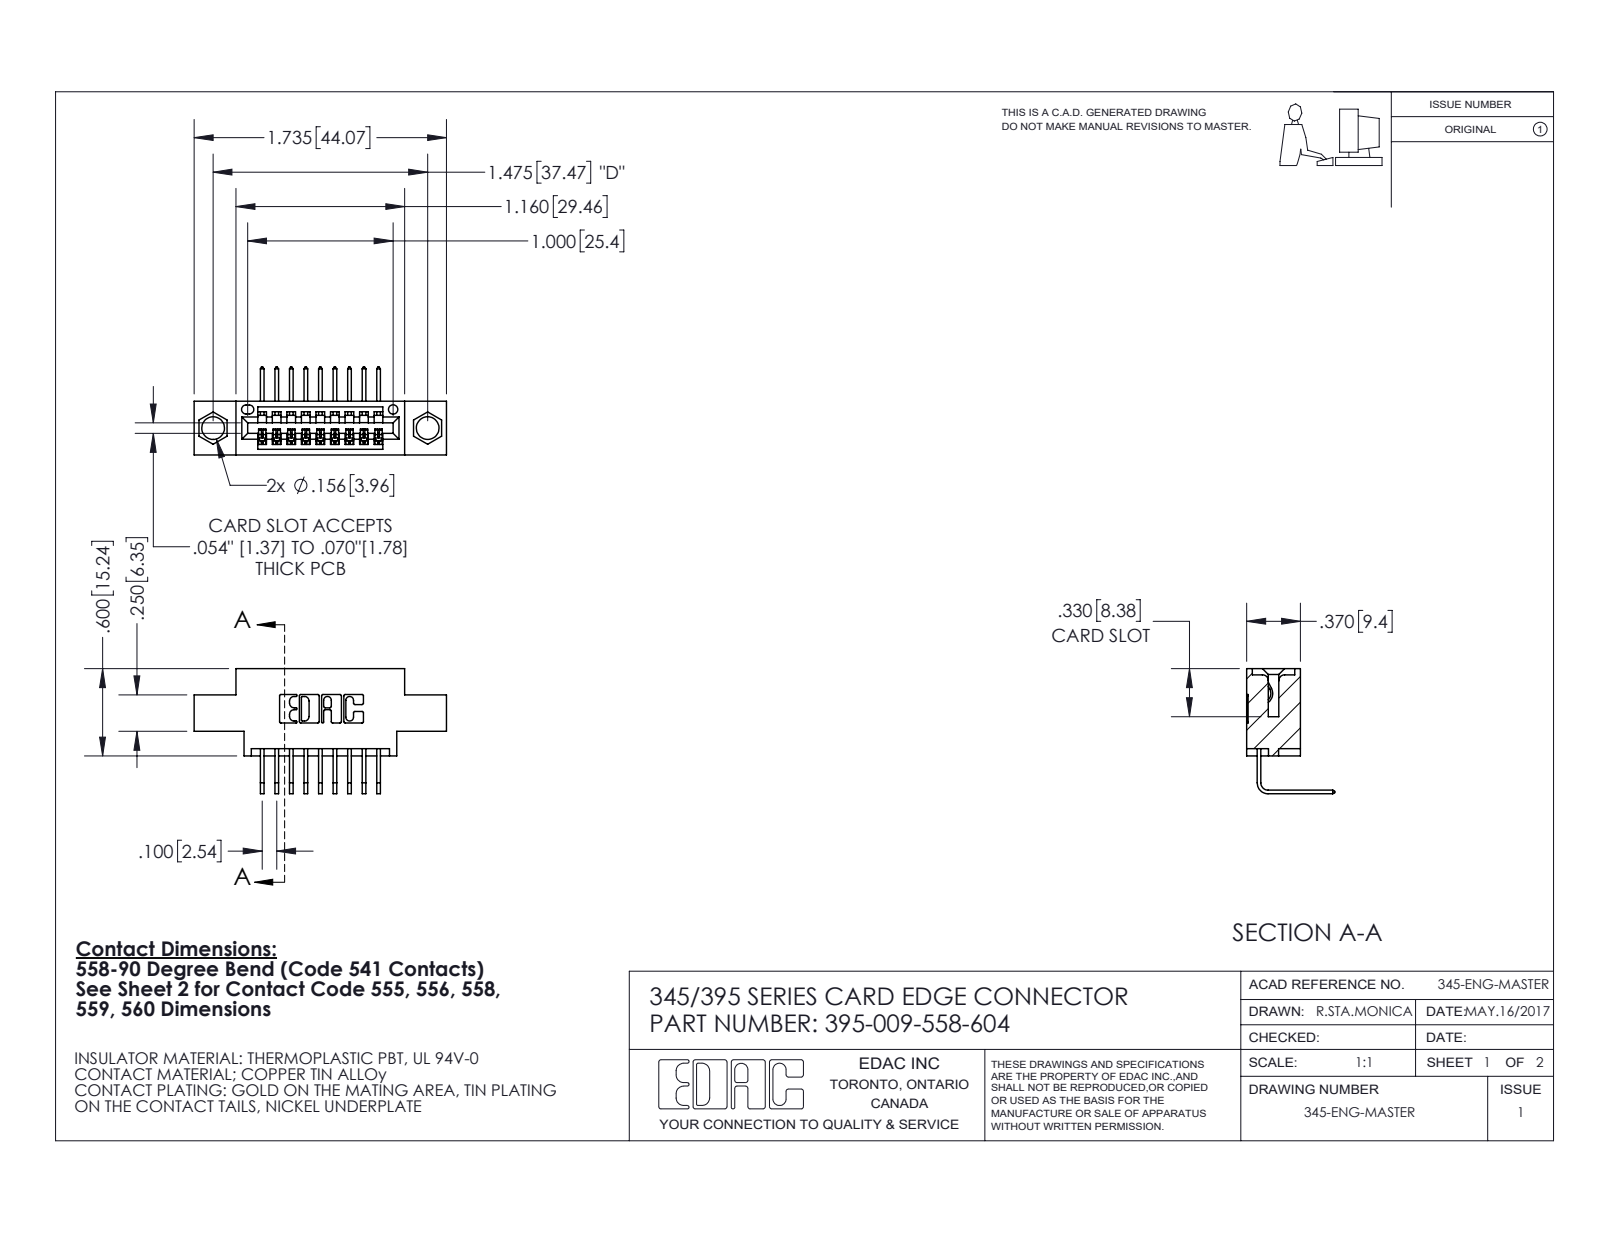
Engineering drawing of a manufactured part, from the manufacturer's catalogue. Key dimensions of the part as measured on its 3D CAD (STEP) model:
Part name (STEP PRODUCT): 345-292-001_558 Tail - 2; 345 Part_0.170 Offset - 0.156 Dia-TI; 395-009-558-604
STEP written by: SolidWorks 2020 (CONFIG_CONTROL_DESIGN)
Units: inches
Bodies: 10 solids, 684 faces (476 planar, 208 cylindrical, 0 other)
Overall size (bounding box): 1.735 × 0.859 × 0.605
Volume: 0.227 in³ · Surface area: 7.205 in²
Round holes (diameter × count): ⌀0.156 ×2, ⌀0.064 ×1
Partial cylindrical surfaces — rounded edges, fillets, slot ends (radius × count): R0.01 ×22, R0.006 ×18, R0.007 ×6, R0.031 ×6, R0.026 ×3, R0.031 ×2, R0.04 ×2, R0.014 ×1
Main face-to-face distances: 0.37, 0.2, 0.072, 0.298, 0.1, 0.098, 0.272, 0.025, 0.3, 0.6
Hole centre spacings: 0.27, 1.244, 1.475
